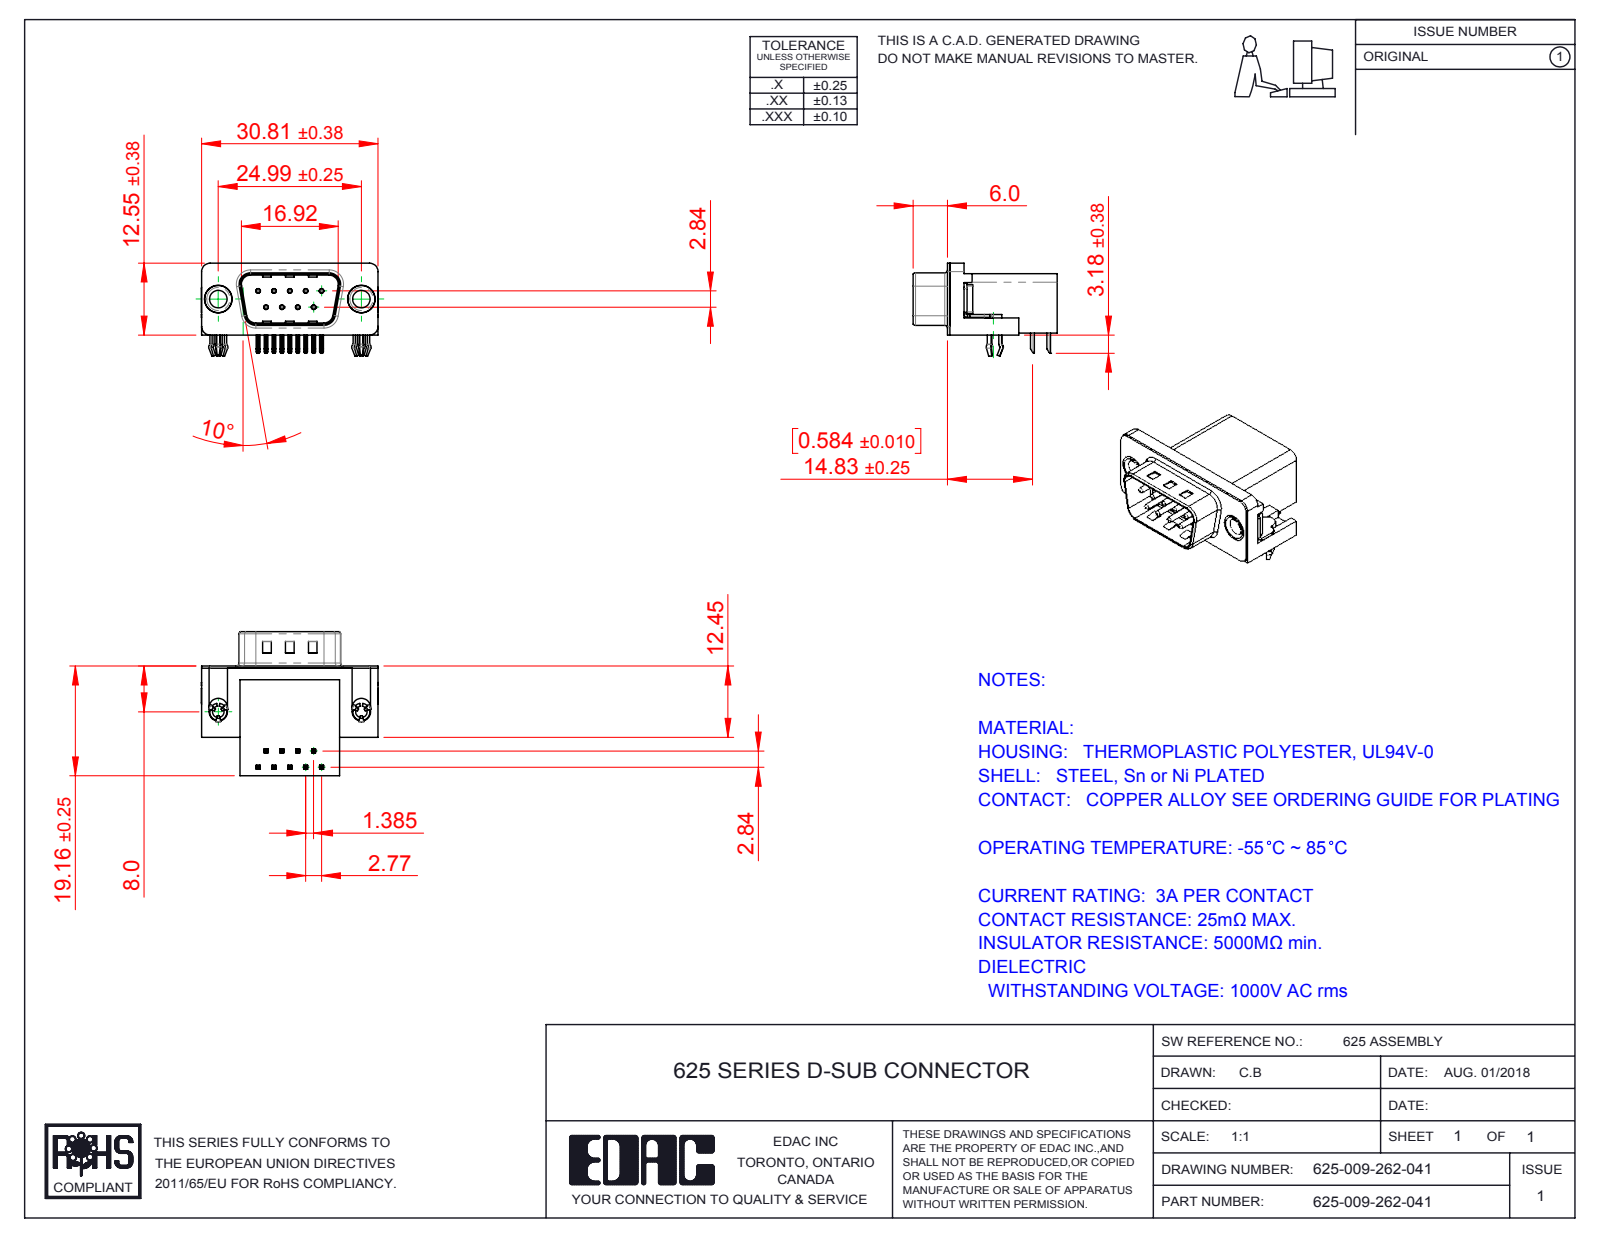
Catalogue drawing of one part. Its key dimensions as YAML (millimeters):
part_name: "625 Contact Bottom; 625 Housing_9 Socket; 625 Contact Top; 625-009-262-041 (+3 more)"
step_written_by: "SolidWorks 2016 (CONFIG_CONTROL_DESIGN)"
units: millimeters
bodies: {solids: 15, faces: 1057, planar: 611, cylindrical: 305, other: 141}
overall_size: [30.89, 25.16, 16.25]
volume: 4472
surface_area: 4989
round_holes:
  - {diameter: 0.35, count: 9}
  - {diameter: 0.8, count: 9}
  - {diameter: 2, count: 2}
  - {diameter: 3.05, count: 2}
  - {diameter: 4, count: 2}
  - {diameter: 4.8, count: 2}
  - {diameter: 5, count: 2}
round_bosses_or_shafts:
  - {diameter: 0.75, count: 9}
  - {diameter: 4.9, count: 2}
  - {diameter: 4.75, count: 2}
  - {diameter: 3.85, count: 2}
  - {diameter: 3, count: 2}
partial_cylinders:
  - {radius: 0.25, count: 48}
  - {radius: 0.12, count: 18}
  - {radius: 1, count: 16}
  - {radius: 0.5, count: 9}
  - {radius: 1.5, count: 8}
  - {radius: 1.6, count: 8}
  - {radius: 0.9, count: 4}
  - {radius: 2, count: 4}
face_to_face_distances: [0.4, 10.34, 18.76, 19.16, 2.9, 16.26, 2.5, 0.35, 10.69, 6.7]
hole_center_spacings: [3.16, 2.77, 5.54, 5.03, 5.04, 8.31, 7.48, 7.49]
